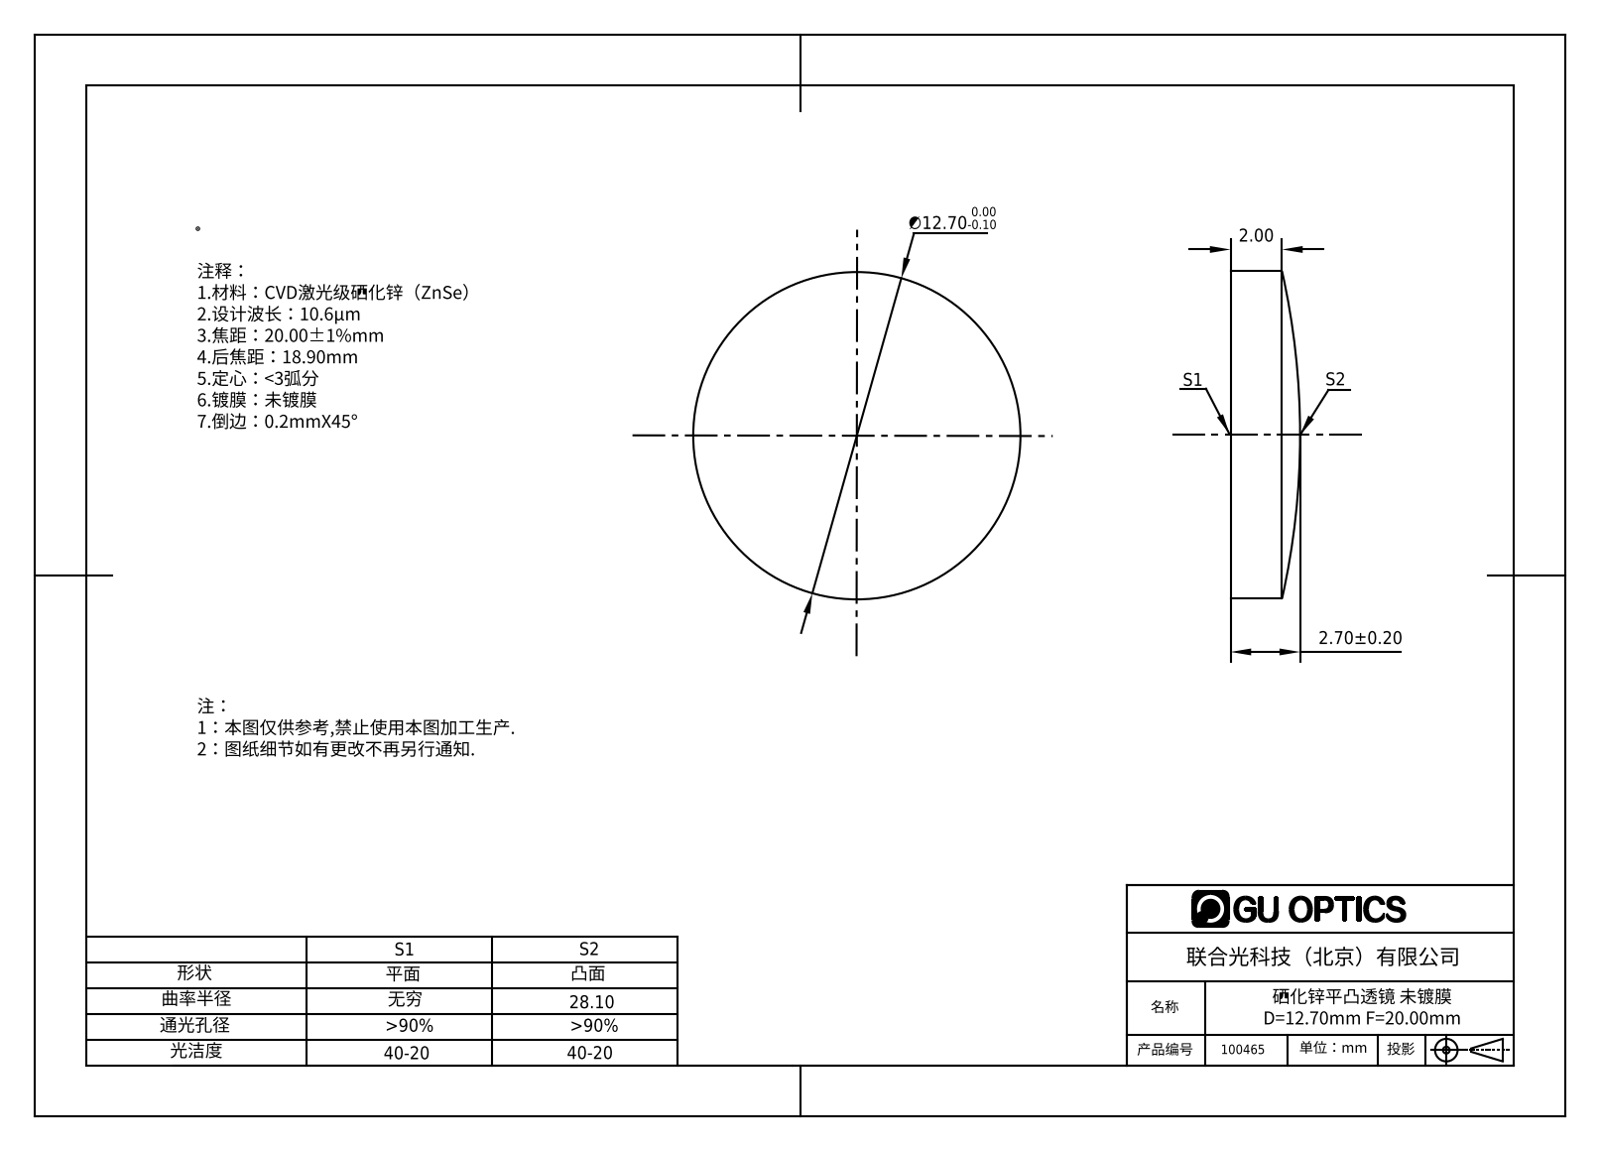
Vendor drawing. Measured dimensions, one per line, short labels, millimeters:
name: 100456
written by: SolidWorks 2016 (AUTOMOTIVE_DESIGN)
unit: mm
bodies: 1 solid, 5 faces (1 planar, 2 cylindrical, 2 other)
size: 12.7 × 12.7 × 2.7
volume: 298 mm³; area: 335 mm²
bosses: 1× ⌀12.7
